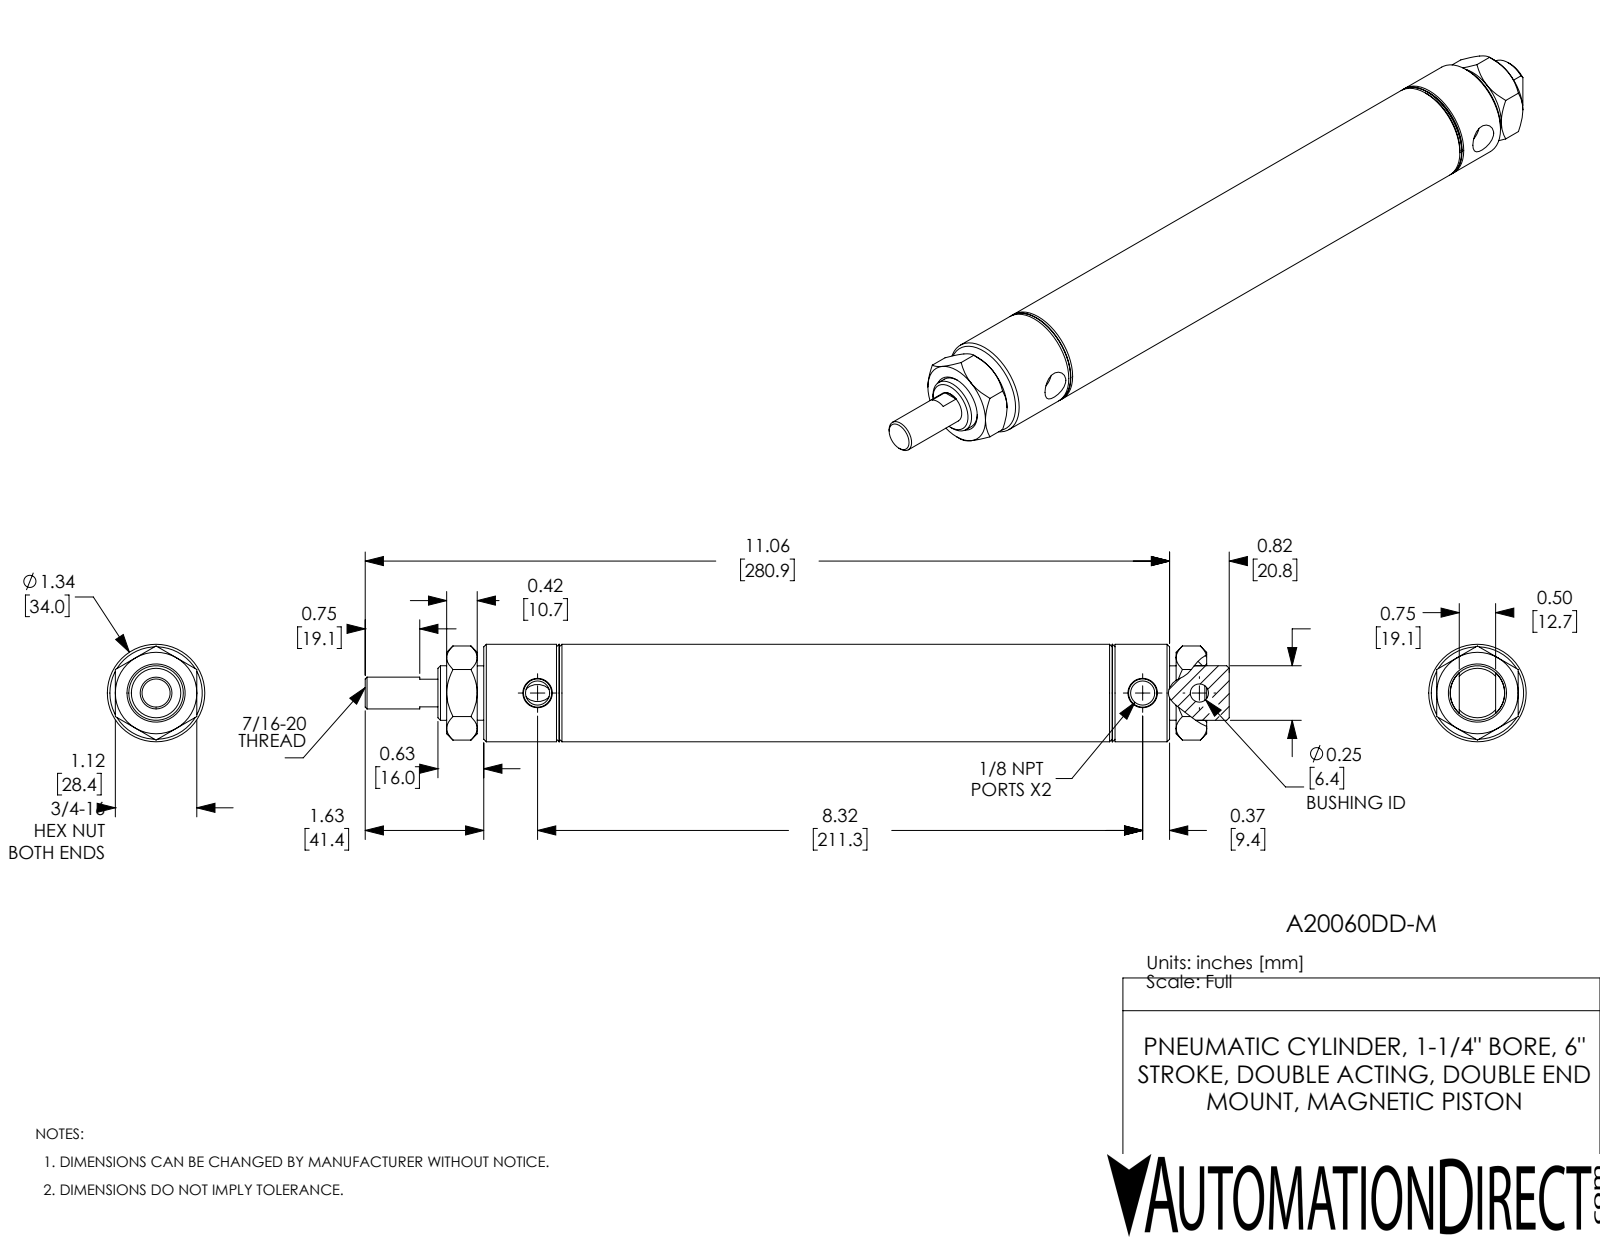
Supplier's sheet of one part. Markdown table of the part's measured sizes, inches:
| quantity | value |
| --- | --- |
| part name | A20060DD-M; A20060DD-M_Mounting Nut_D-3556; A20060DD-M-Rod; A20060DD-M-MainBody |
| STEP written by | SolidWorks 2017 (AUTOMOTIVE_DESIGN) |
| units | inches |
| bodies | 4 solids, 138 faces (44 planar, 36 cylindrical, 58 other) |
| overall size | 11.88 × 1.34 × 1.34 |
| volume | 7.938 in³ |
| surface area | 102.4 in² |
| round holes (diameter × count) | 0.332 × 2, 0.251 × 1, 0.437 × 1, 0.75 × 1, 1.25 × 1 |
| round bosses / shafts (diameter × count) | 1.34 × 1, 0.747 × 1 |
| main face-to-face distances | 1.465, 7.965, 0.5, 1.12, 6.5, 6, 0.31, 0.42, 10.03, 1.965 |
| hole center spacings | 0.78, 8.32, 9.1 |
